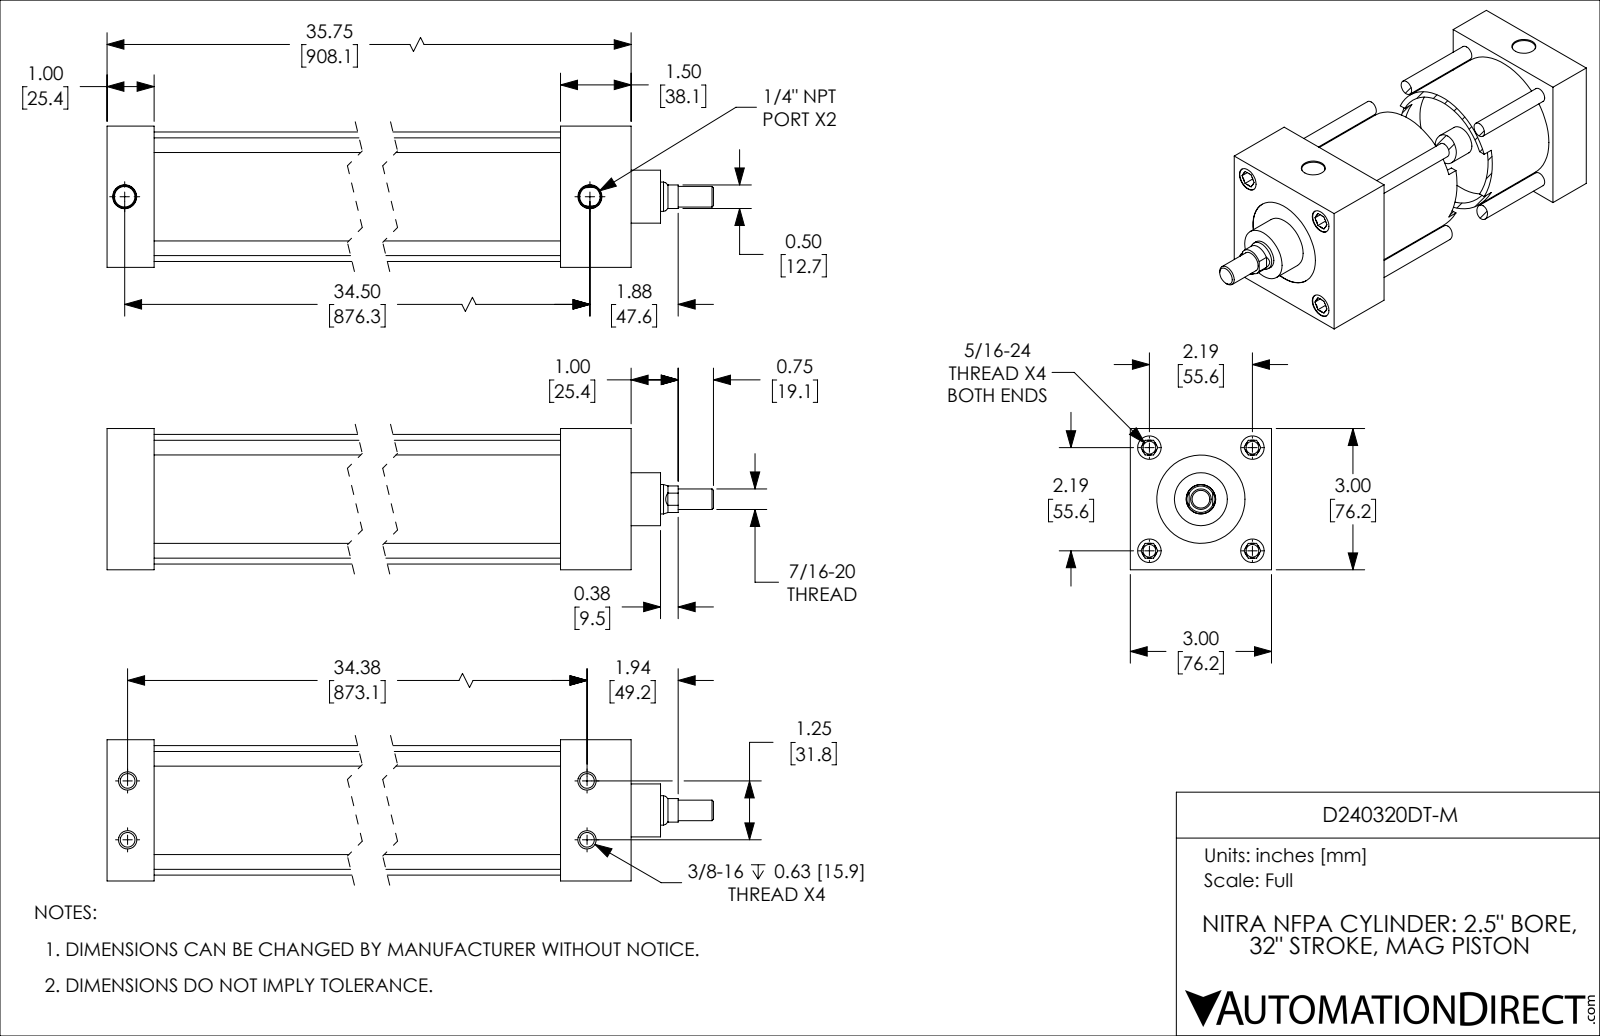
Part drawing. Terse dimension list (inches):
name: D240320DT-M; D240320DT-M_PISTON_KK1; D240320DT-M_BODY
written by: SolidWorks 2019 (CONFIG_CONTROL_DESIGN)
unit: in
bodies: 2 solids, 200 faces (58 planar, 62 cylindrical, 80 other)
size: 37.5 × 3 × 3
volume: 82.61 in³; area: 848.3 in²
holes: 4× ⌀0.272, 4× ⌀0.313, 4× ⌀0.5, 2× ⌀0.438, 1× ⌀0.626, 1× ⌀1.875, 1× ⌀2.501
bosses: 4× ⌀0.312, 1× ⌀2.751, 1× ⌀2.499, 1× ⌀1.125, 1× ⌀0.624, 1× ⌀0.437
rounds: 1× R0.281
face distances: 3, 1, 34.25, 33.25, 35.75, 34.75, 1.5, 1.25, 2.25, 32
hole spacings: 1.548, 2.19, 34.443, 0.628, 0.628, 1.25, 3.097, 34.375
